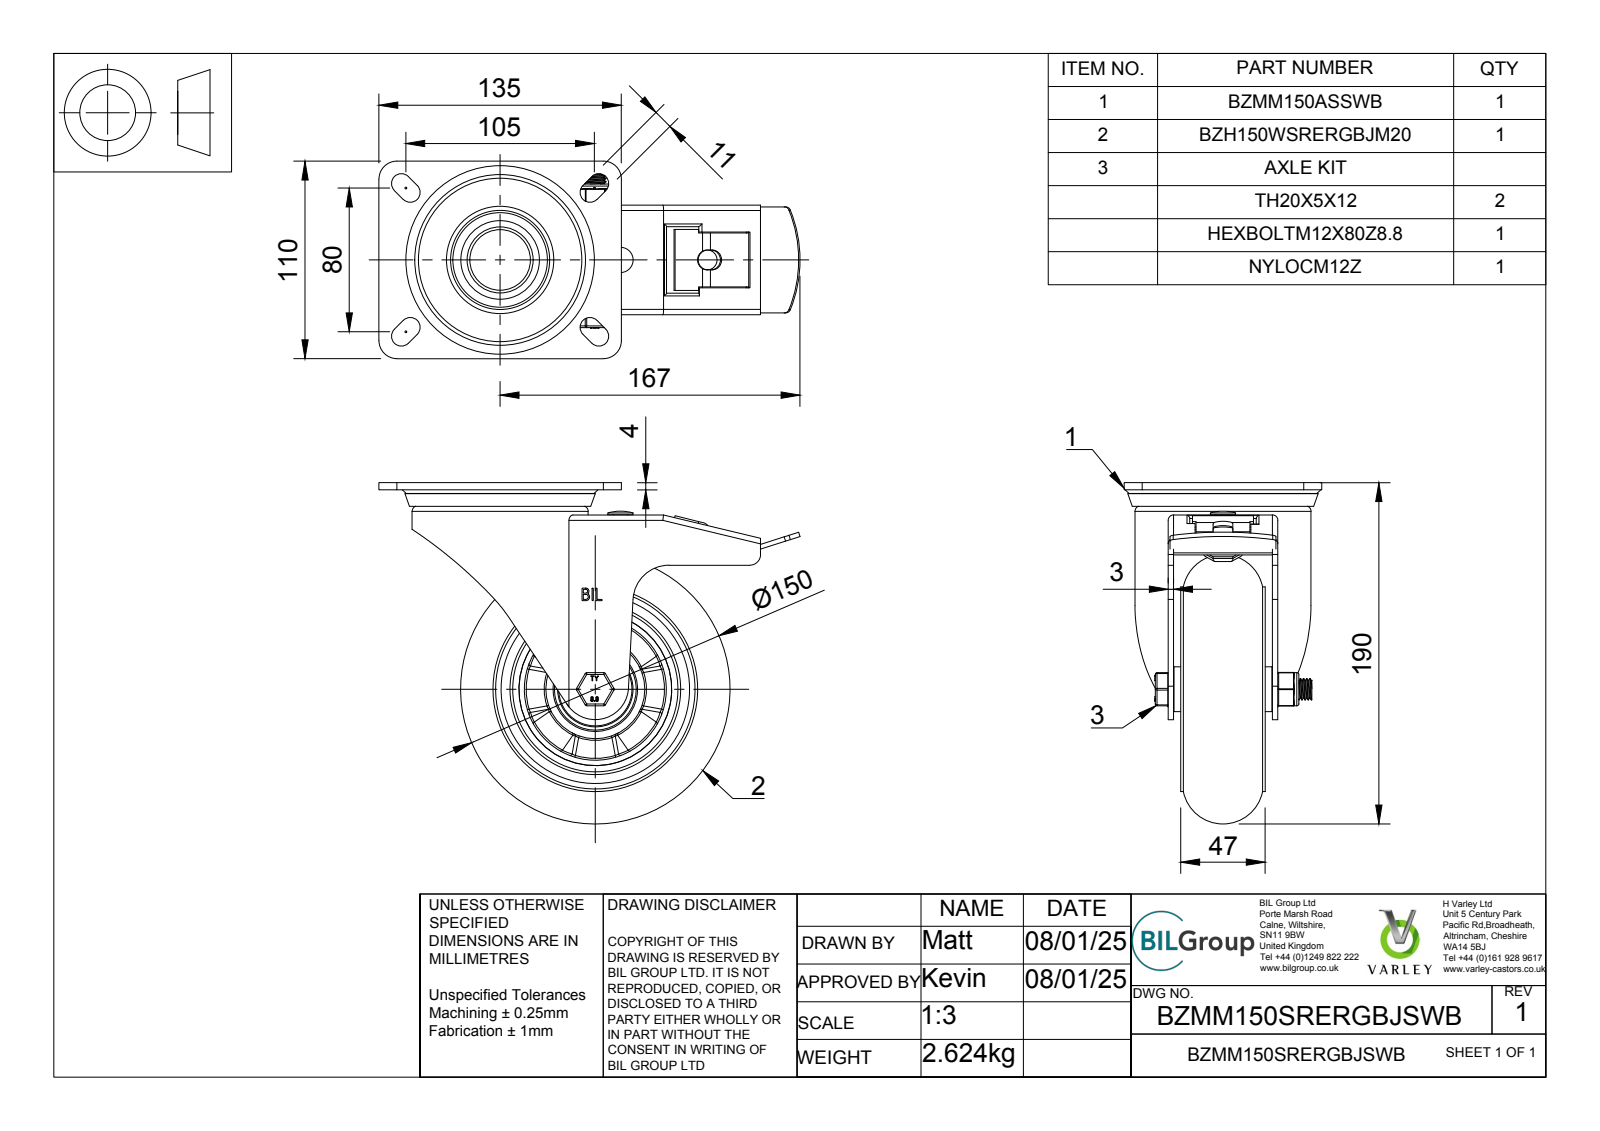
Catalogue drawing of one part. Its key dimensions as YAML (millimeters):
part_name: "BZMM150SRERGBJSWB v3; BZMM150ASSWB - 55 v1; ZINC PLATED, PRESSED STEEL TOP PLATE; ZINC PLATED, PRESSED STEEL TOP PLATE Geometry (+7 more)"
step_written_by: "Autodesk Translation Framework v13.20.0.188 (AP242_MANAGED_MODEL_BASED_3D_ENGINEERING_MIM_LF)"
units: millimeters
bodies: {solids: 82, faces: 1428, planar: 551, cylindrical: 256, other: 621}
overall_size: [234.5, 190, 110]
volume: 767242
surface_area: 282534
round_holes:
  - {diameter: 92, count: 2}
  - {diameter: 8, count: 1}
  - {diameter: 11, count: 1}
  - {diameter: 12, count: 1}
  - {diameter: 12.2, count: 1}
  - {diameter: 12.5, count: 1}
  - {diameter: 14, count: 1}
  - {diameter: 20, count: 1}
  - {diameter: 28.5, count: 1}
  - {diameter: 30.8, count: 1}
  - {diameter: 33.75, count: 1}
  - {diameter: 39.75, count: 1}
round_bosses_or_shafts:
  - {diameter: 114, count: 1}
  - {diameter: 98, count: 1}
  - {diameter: 95, count: 1}
  - {diameter: 78, count: 1}
  - {diameter: 55, count: 1}
  - {diameter: 50, count: 1}
  - {diameter: 40.8, count: 1}
  - {diameter: 31.3, count: 1}
partial_cylinders:
  - {radius: 0.5, count: 18}
  - {radius: 1, count: 12}
  - {radius: 1.5, count: 10}
  - {radius: 5.5, count: 10}
  - {radius: 0.25, count: 6}
  - {radius: 2.5, count: 6}
  - {radius: 3, count: 6}
  - {radius: 10, count: 4}
face_to_face_distances: [3, 9, 5, 4, 8, 12, 58, 16, 14, 7]
hole_center_spacings: [67]
